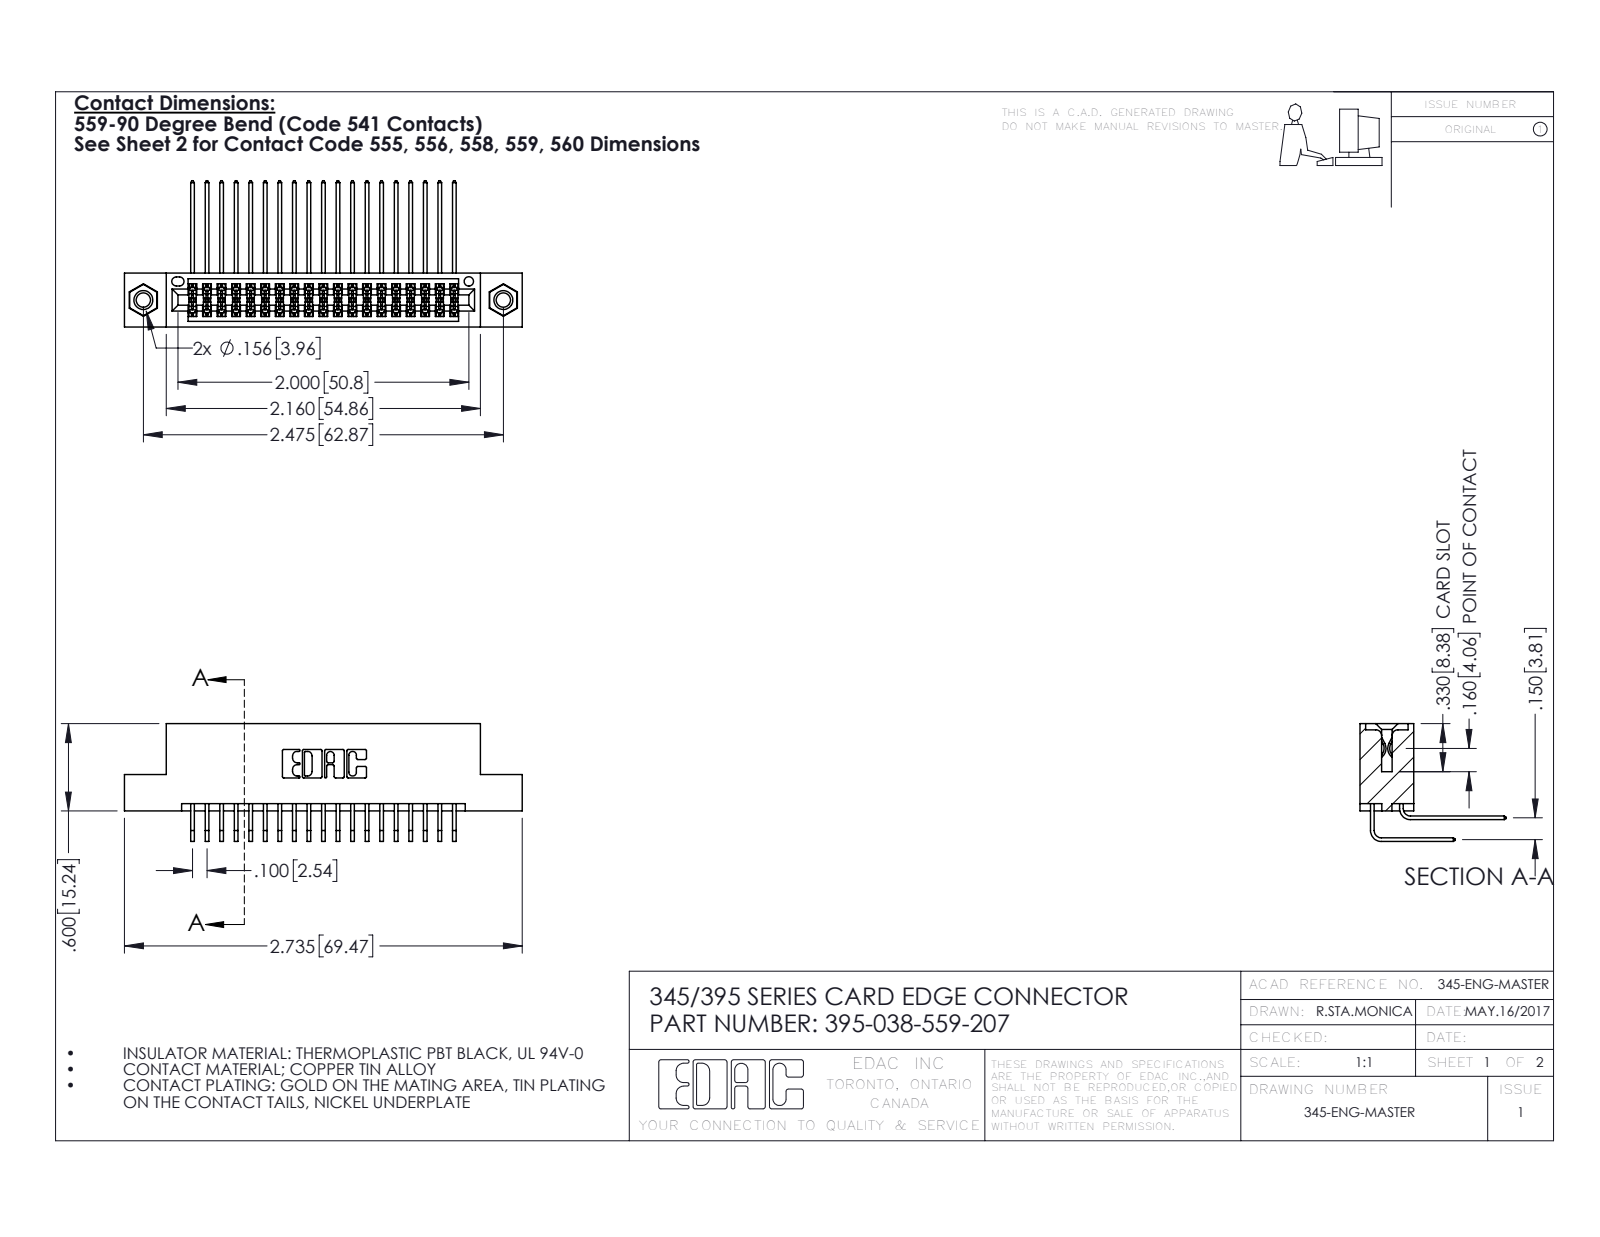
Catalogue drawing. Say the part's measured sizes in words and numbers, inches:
The part is named "345-250-001_345-250-005-103; 345-292-001_559 Tail - 2; 345 Part_Flush Mounting Lugs - 0.156 Dia-TI; 395-038-559-207 (+1 more)". Its 3-D file was written by "SolidWorks 2016 (CONFIG_CONTROL_DESIGN)". It is 41 solids with 2162 faces: 1442 planar, 704 cylindrical and 16 other. Overall it measures 2.735 by 1.005 by 0.809 inches. Its volume is 0.411 cubic inches and its surface area 16.39 square inches. Round holes: 2 of diameter 0.098, 2 of diameter 0.125, 2 of diameter 0.156, 1 of diameter 0.064. Round bosses or shafts: 2 of diameter 0.155. Partial cylindrical surfaces (rounded edges, fillets, slot ends): 58 of radius 0.006, 22 of radius 0.01, 6 of radius 0.007, 6 of radius 0.031, 3 of radius 0.026, 2 of radius 0.014, 2 of radius 0.019, 2 of radius 0.022. The main face-to-face distances are 0.072, 0.298, 0.2, 0.37, 0.098, 0.272, 0.025, 0.225, 0.15, 0.175. The hole center spacings are 0.27, 2.241, 2.475.
